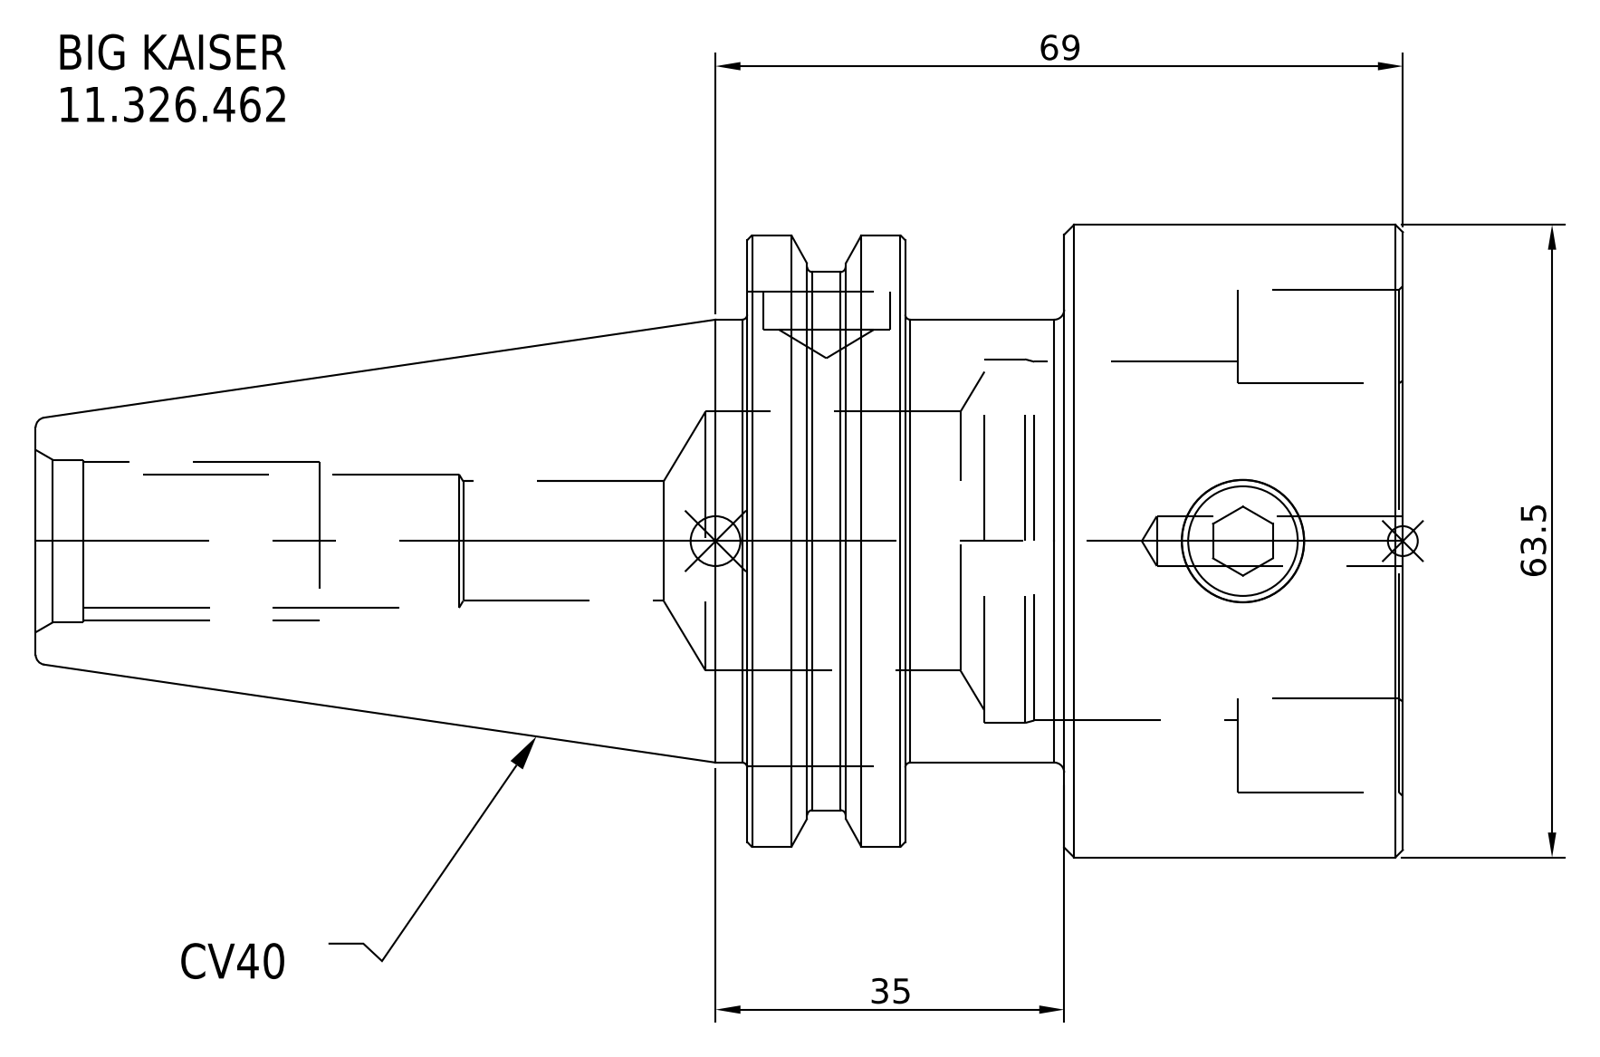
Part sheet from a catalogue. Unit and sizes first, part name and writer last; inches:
Units: inches
Overall size (bounding box): 5.404 × 2.5 × 2.5
Round bosses / shafts (diameter × count): ⌀2.5 ×1, ⌀2.491 ×1, ⌀2.219 ×1, ⌀1.75 ×1
Main face-to-face distances: 1.337, 2.592, 1.255, 1.967, 0.63, 0.625, 5.404, 4.067, 3.437, 2.812
Volume: 15.19 in³ · Surface area: 50.21 in²
Bodies: 2 solids, 17 faces (8 planar, 6 cylindrical, 3 other)
Part name (STEP PRODUCT): 11_326_462
STEP written by: SolidWorks 2021 (CONFIG_CONTROL_DESIGN)
